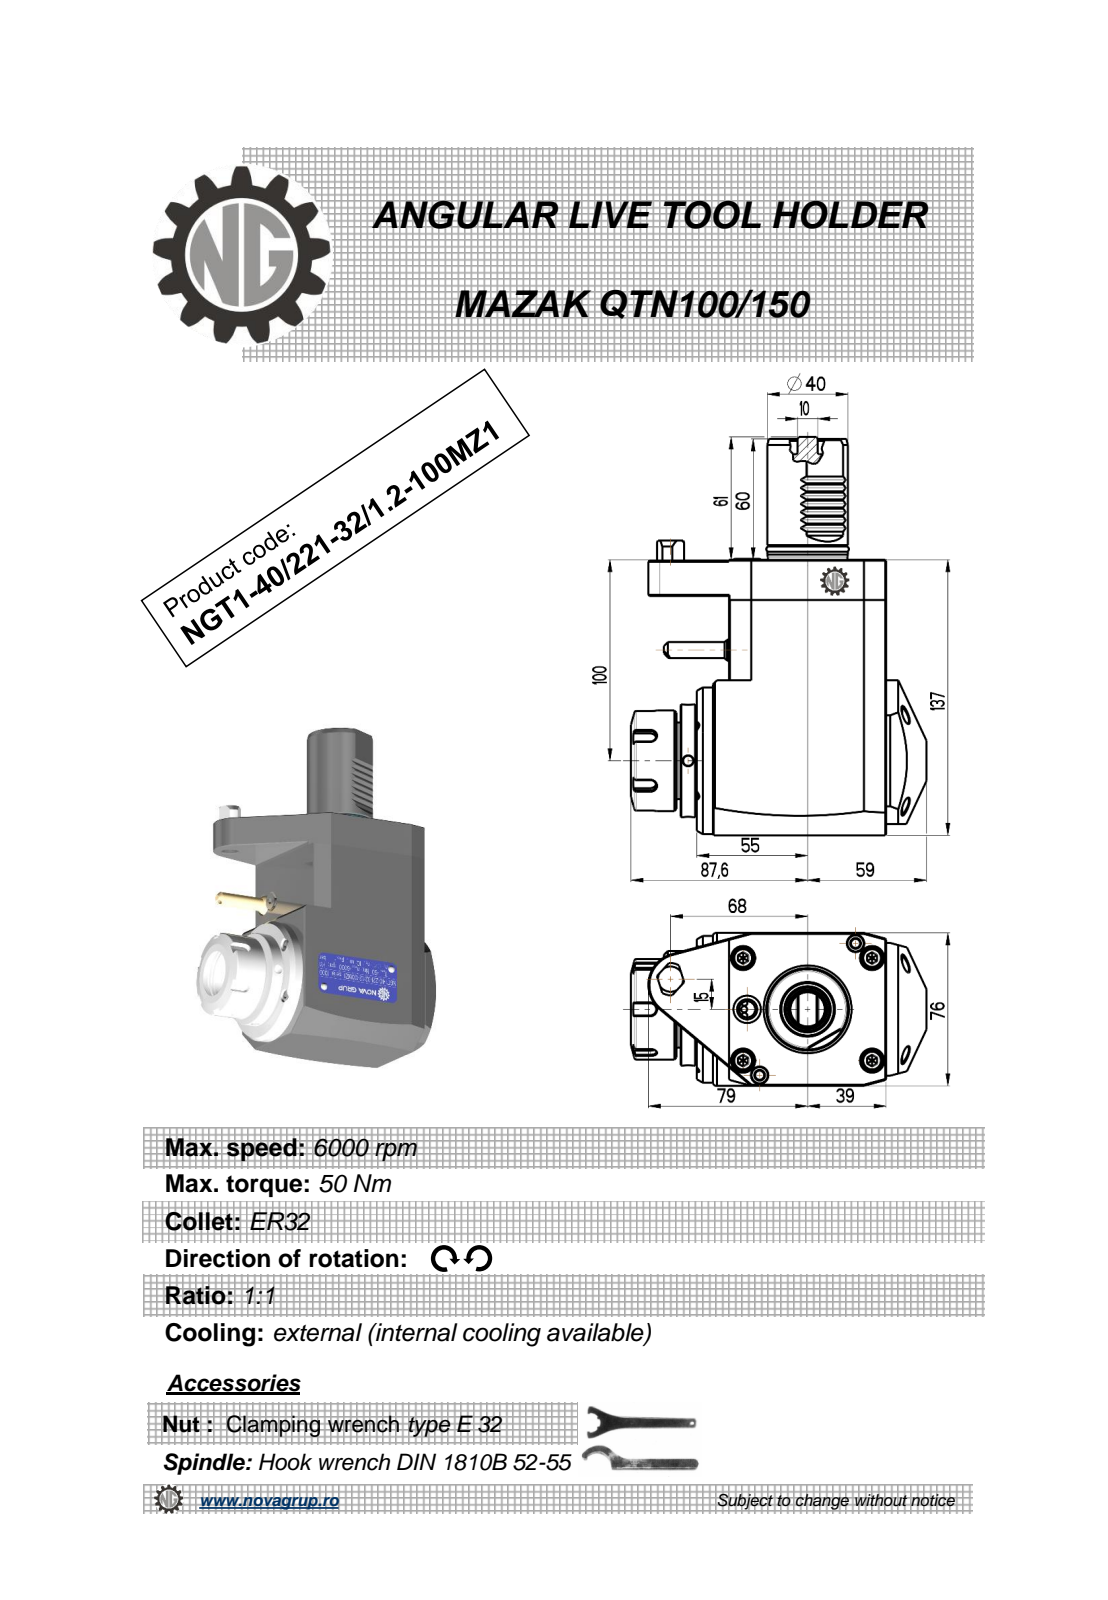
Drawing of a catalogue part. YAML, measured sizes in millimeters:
part_name: "NGT1_40_221_32_1_2_100MZ1"
step_written_by: "PRO/ENGINEER BY PARAMETRIC TECHNOLOGY CORPORATION, 2010280 (CONFIG_CONTROL_DESIGN)"
units: millimeters
bodies: {solids: 1, faces: 305, planar: 138, cylindrical: 76, other: 91}
overall_size: [198, 146.6, 76]
volume: 1090000
surface_area: 81974
round_holes:
  - {diameter: 5, count: 3}
  - {diameter: 3, count: 1}
  - {diameter: 8, count: 1}
  - {diameter: 26, count: 1}
  - {diameter: 27, count: 1}
round_bosses_or_shafts:
  - {diameter: 73, count: 1}
  - {diameter: 56, count: 1}
  - {diameter: 50, count: 1}
  - {diameter: 43, count: 1}
  - {diameter: 40, count: 1}
  - {diameter: 39.4, count: 1}
  - {diameter: 36.2, count: 1}
  - {diameter: 10, count: 1}
partial_cylinders:
  - {radius: 0.3, count: 7}
  - {radius: 0.2, count: 6}
  - {radius: 3, count: 5}
  - {radius: 0.8, count: 2}
  - {radius: 300, count: 2}
  - {radius: 8, count: 1}
  - {radius: 9, count: 1}
  - {radius: 15.84, count: 1}
face_to_face_distances: [76, 137, 8, 78, 16, 94, 18, 87.92, 119, 7.5]
hole_center_spacings: [29.25, 30, 59.25, 60.42]
